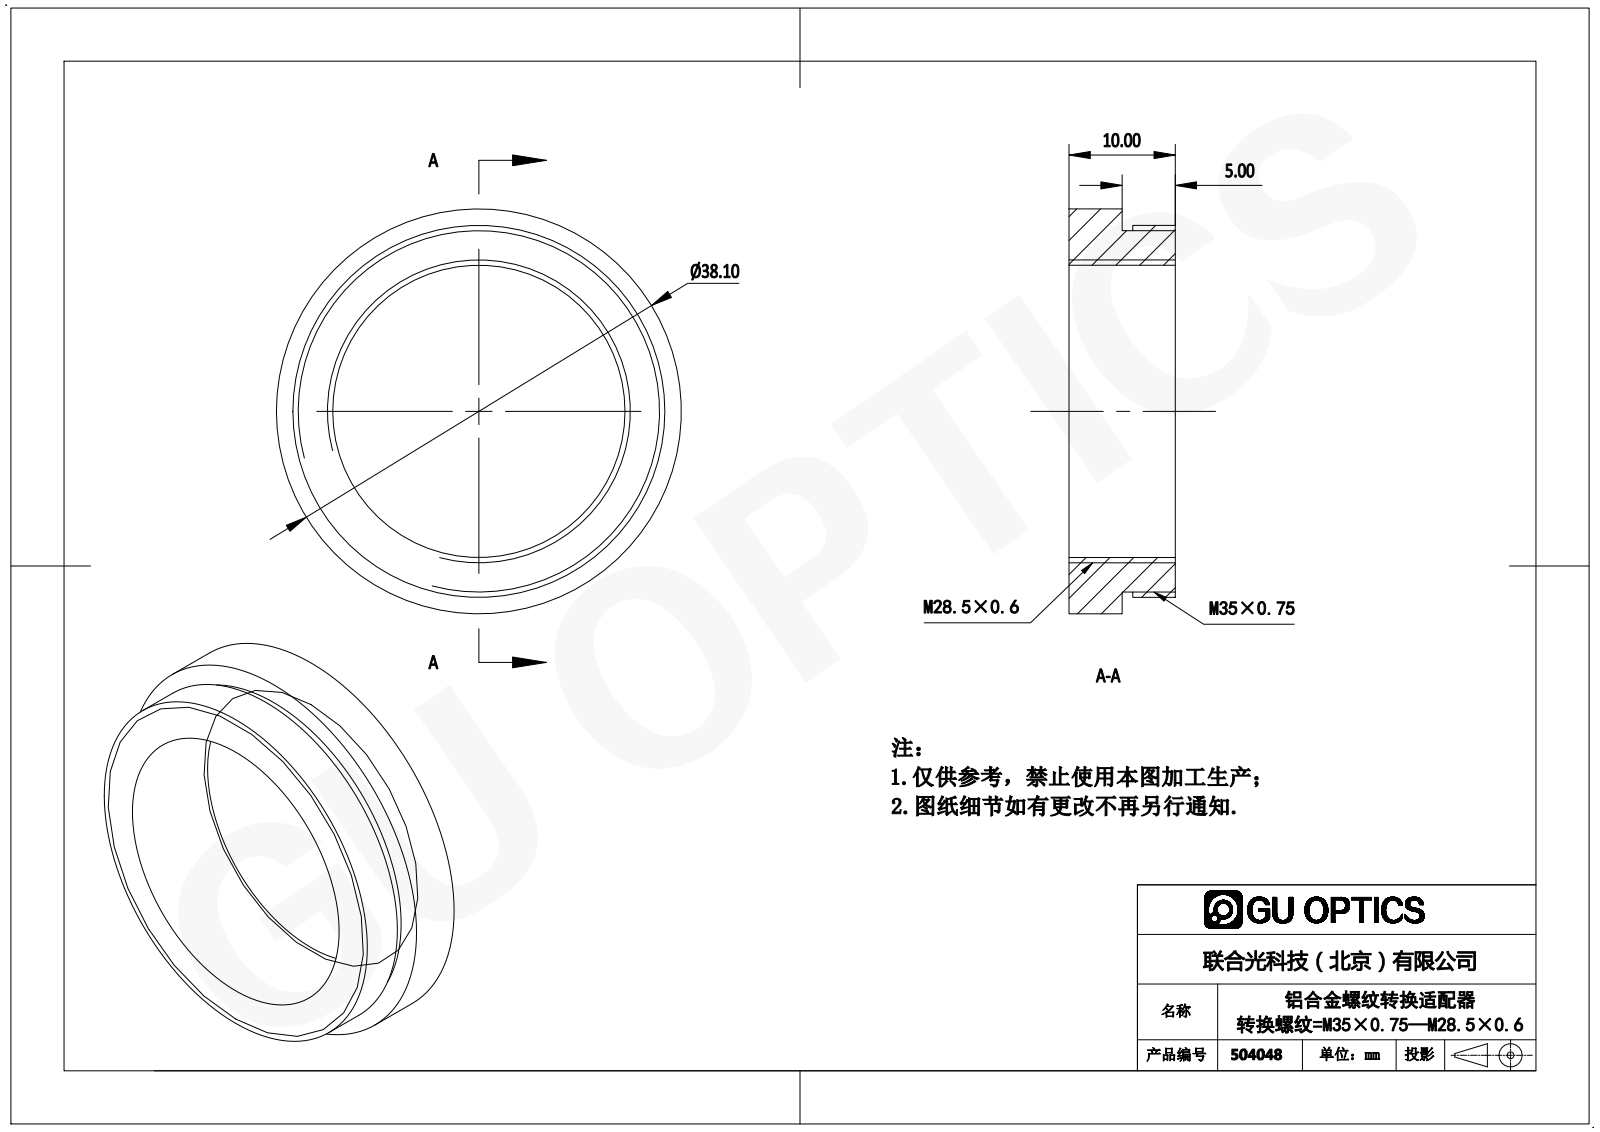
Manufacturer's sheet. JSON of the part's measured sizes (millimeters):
{"part_name": "504048", "step_written_by": "SolidWorks 2016 (AUTOMOTIVE_DESIGN)", "units": "millimeters", "bodies": {"solids": 1, "faces": 12, "planar": 4, "cylindrical": 8, "other": 0}, "overall_size": [38.1, 38.1, 10], "volume_mm3": 4517, "surface_area_mm2": 3210, "round_holes": [[27.5, 1]], "round_bosses_or_shafts": [[38.1, 1], [35, 1], [34, 1]], "face_to_face_distances": [5, 10, 6, 1, 4]}
